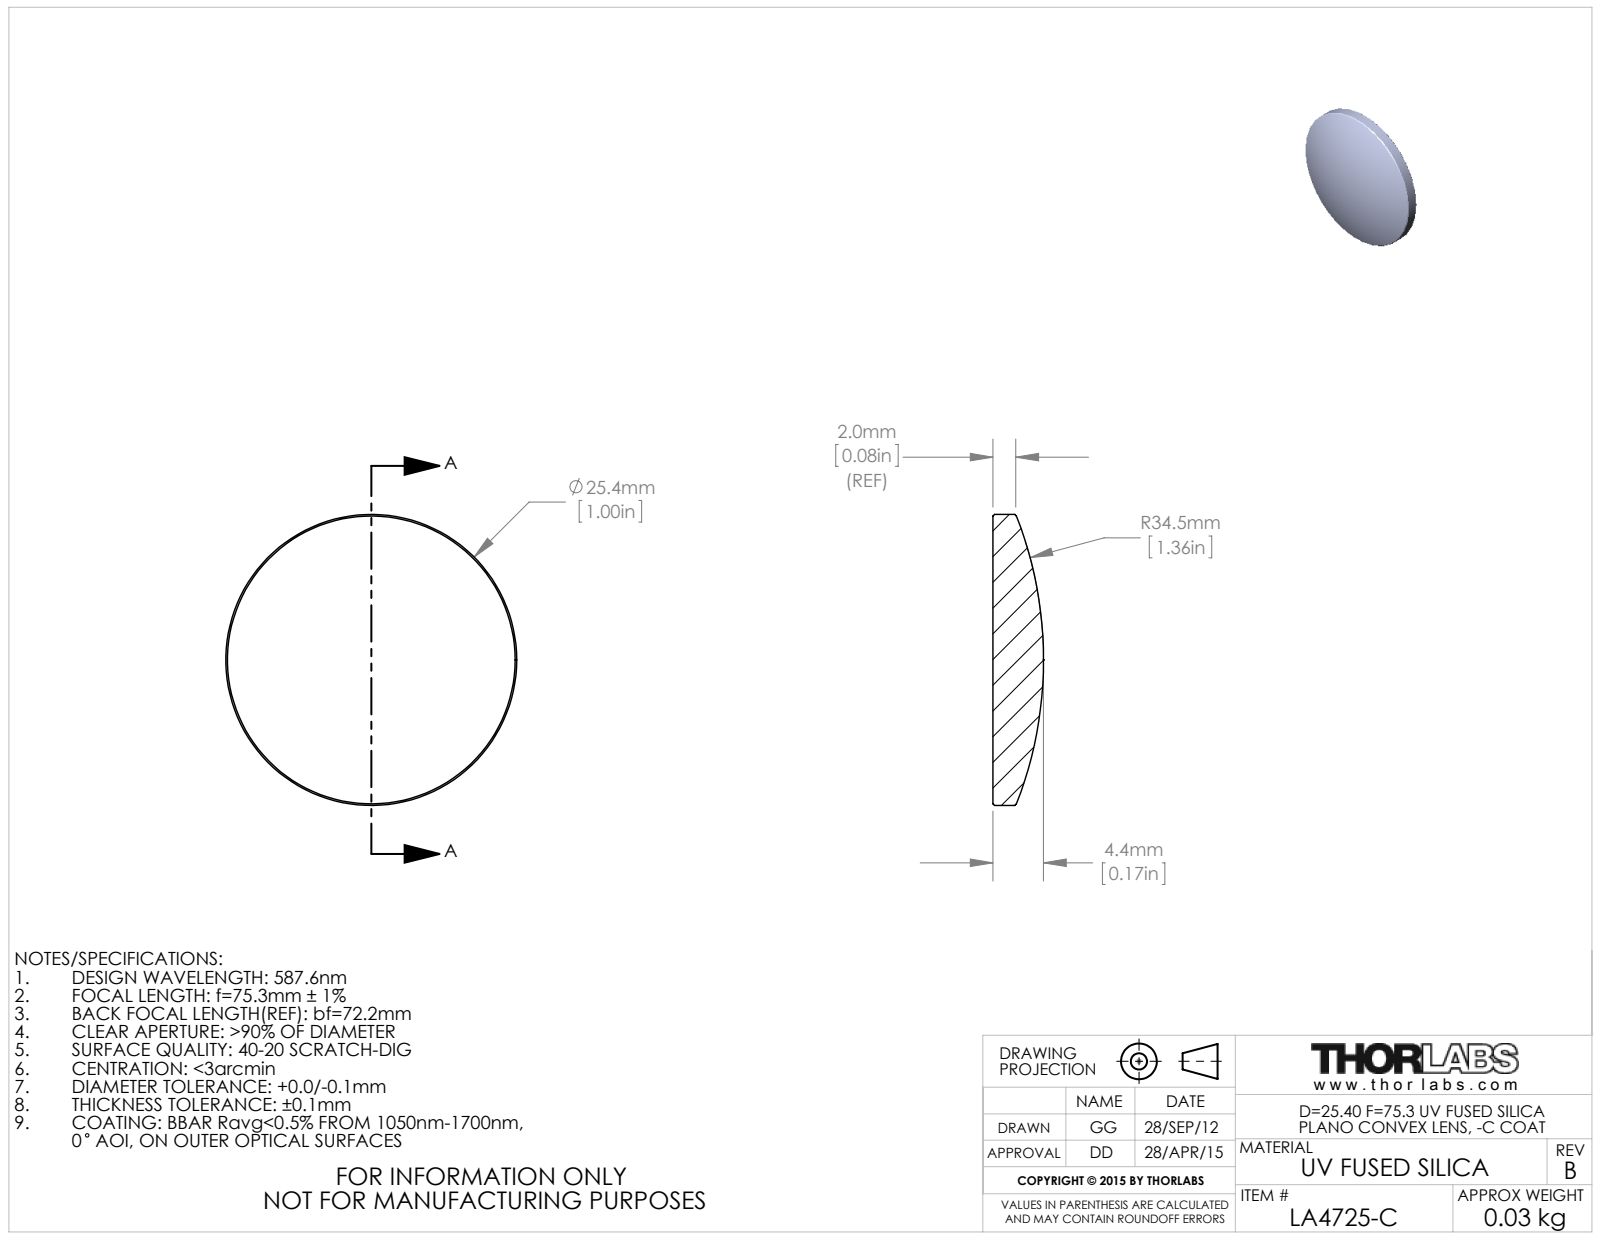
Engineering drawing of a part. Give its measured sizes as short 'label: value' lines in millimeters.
name: 24986-E0W
written by: SolidWorks 2014 (CONFIG_CONTROL_DESIGN)
unit: mm
bodies: 1 solid, 9 faces (1 planar, 2 cylindrical, 6 other)
size: 25.4 × 25.4 × 4.42
volume: 1 633 mm³; area: 1 182 mm²
bosses: 1× ⌀25.4
